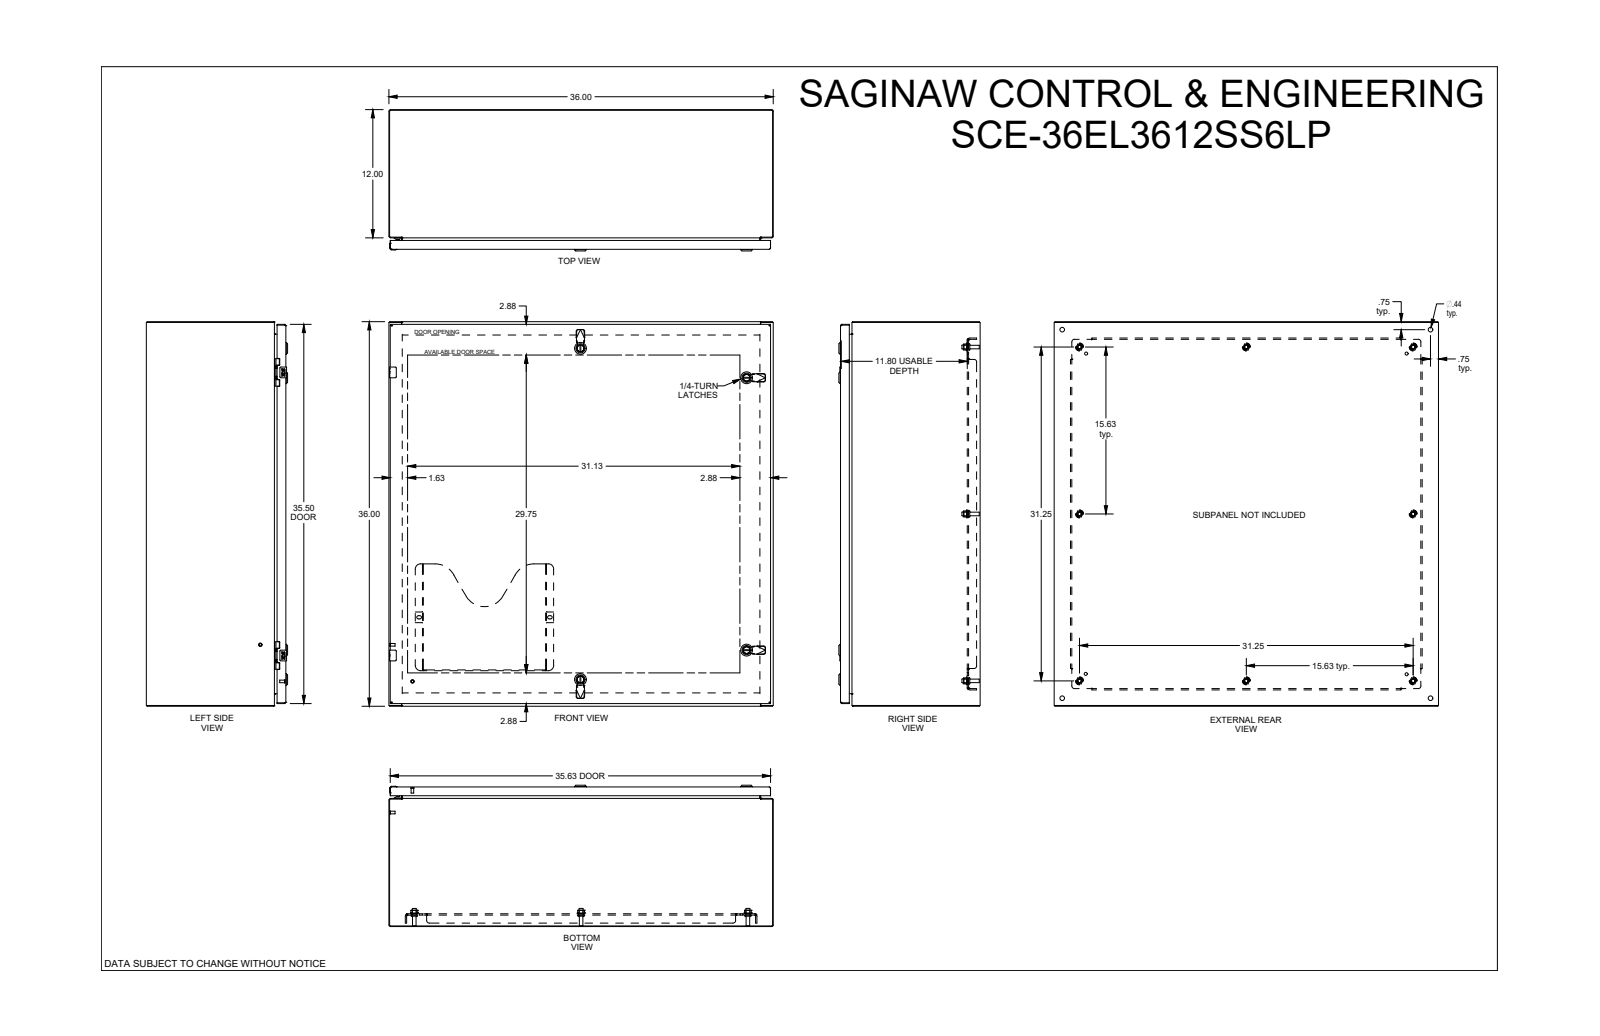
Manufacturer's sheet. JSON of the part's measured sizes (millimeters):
{"part_name": "SCE-36EL3612LP", "step_written_by": "SolidWorks 2021 (AUTOMOTIVE_DESIGN)", "units": "millimeters", "bodies": {"solids": 65, "faces": 3849, "planar": 1489, "cylindrical": 1198, "other": 1162}, "overall_size": [914.4, 914.4, 336], "volume_mm3": 8505000, "surface_area_mm2": 7955000, "round_holes": [[9.3, 8], [12.7, 8], [4.4, 4], [5, 4], [5.2, 4], [6.2, 4], [6.8, 4], [7.1, 4], [8, 4], [9.5, 4], [10, 4], [11.1, 4]], "round_bosses_or_shafts": [[9.3, 8], [8.4, 8], [4.3, 6], [28, 4], [19.8, 4], [16, 4], [13.5, 4], [12.8, 4]], "partial_cylinders_radius": [[0.3, 110], [0.3, 52], [0.5, 44], [0.4, 20], [1, 17], [4, 16], [1.5, 13], [0.7, 12]], "face_to_face_distances": [1.9, 912.5, 1.9, 1.5, 332.1, 330.1, 330.5, 328.6, 30.5, 301.6], "hole_center_spacings": [440.1, 943, 25, 381.5, 673.1, 821.3, 866.4, 0.5]}
